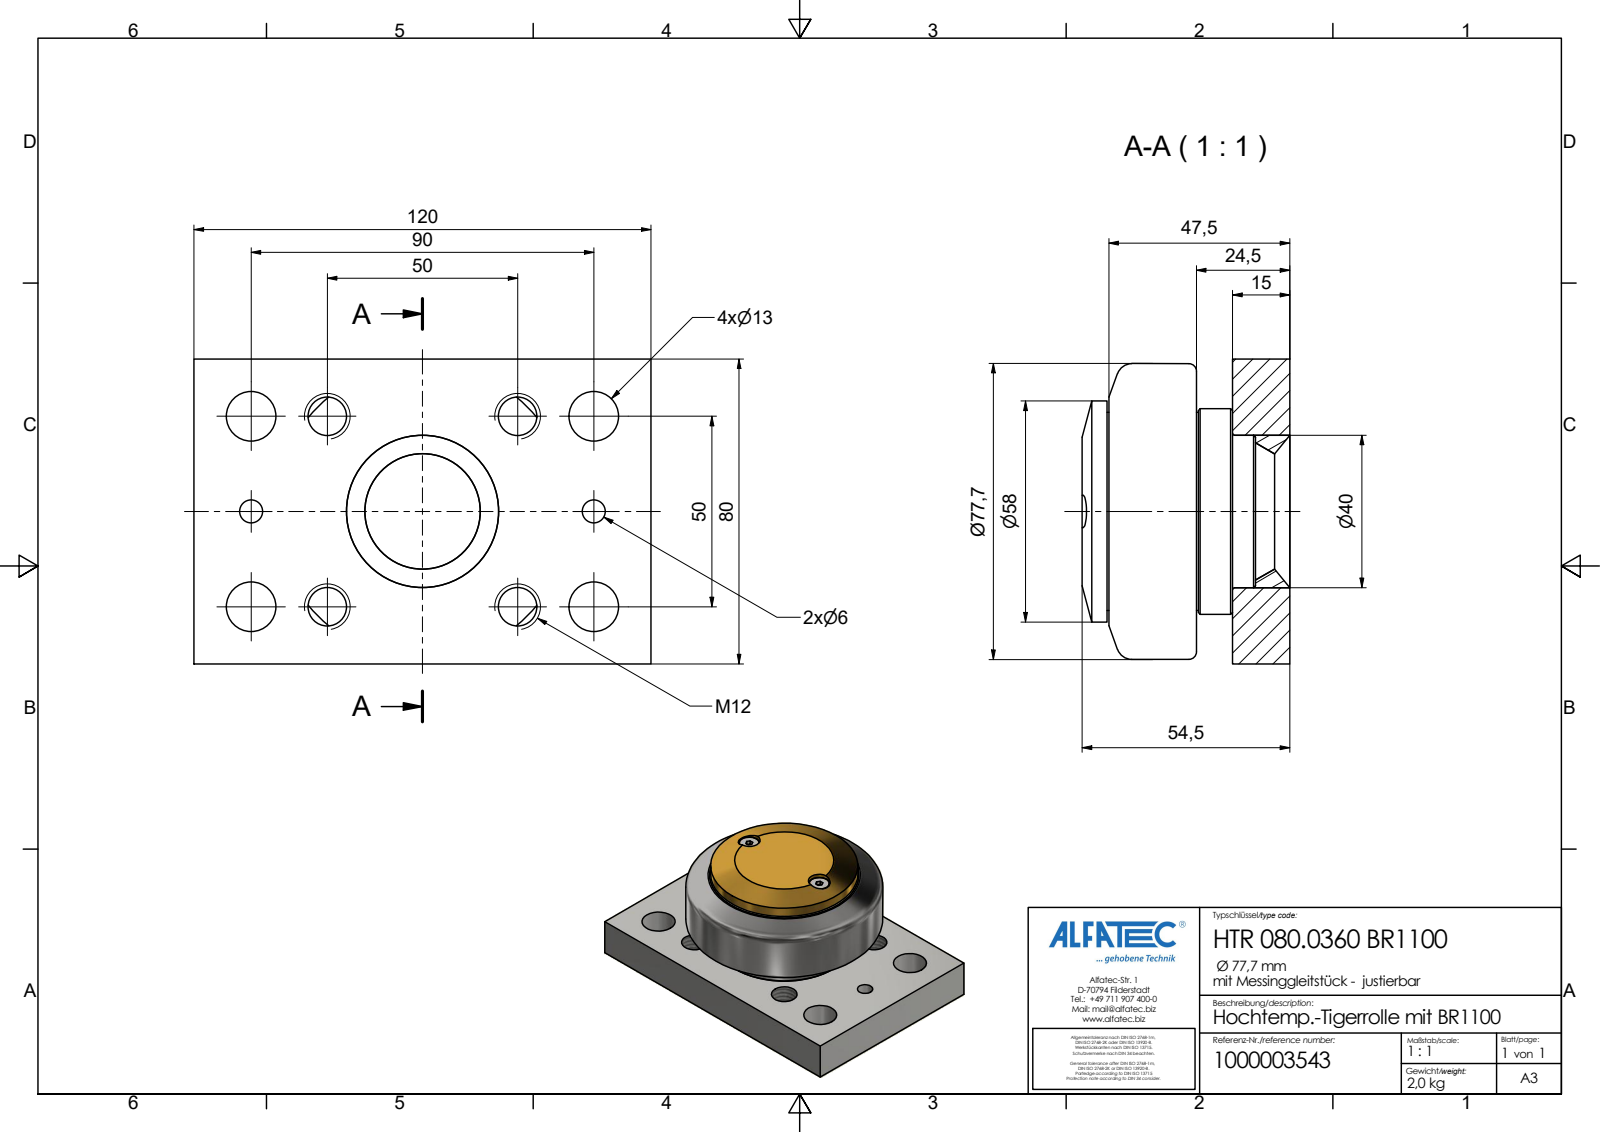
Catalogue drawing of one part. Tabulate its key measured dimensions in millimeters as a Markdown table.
| quantity | value |
| --- | --- |
| part name | HTR 080.0360 BR1100_Kontur |
| STEP written by | Autodesk Inventor 2020 (AP242_MANAGED_MODEL_BASED_3D_ENGINEERING_MIM_LF) |
| units | millimeters |
| bodies | 1 solid, 56 faces (28 planar, 18 cylindrical, 10 other) |
| overall size | 120 × 80 × 54.5 |
| volume | 269 426 mm³ |
| surface area | 41 923 mm² |
| round holes (diameter × count) | 10.11 × 4, 13 × 4, 6 × 2, 8.6 × 2 |
| round bosses / shafts (diameter × count) | 7.8 × 2, 58 × 1, 54 × 1, 52 × 1 |
| main face-to-face distances | 15, 24.5, 9.5, 80, 120, 54.5, 39.5, 30, 4, 11 |
| hole center spacings | 50, 20, 25, 25.6, 32.02, 35.71, 51.04, 53.85 |
